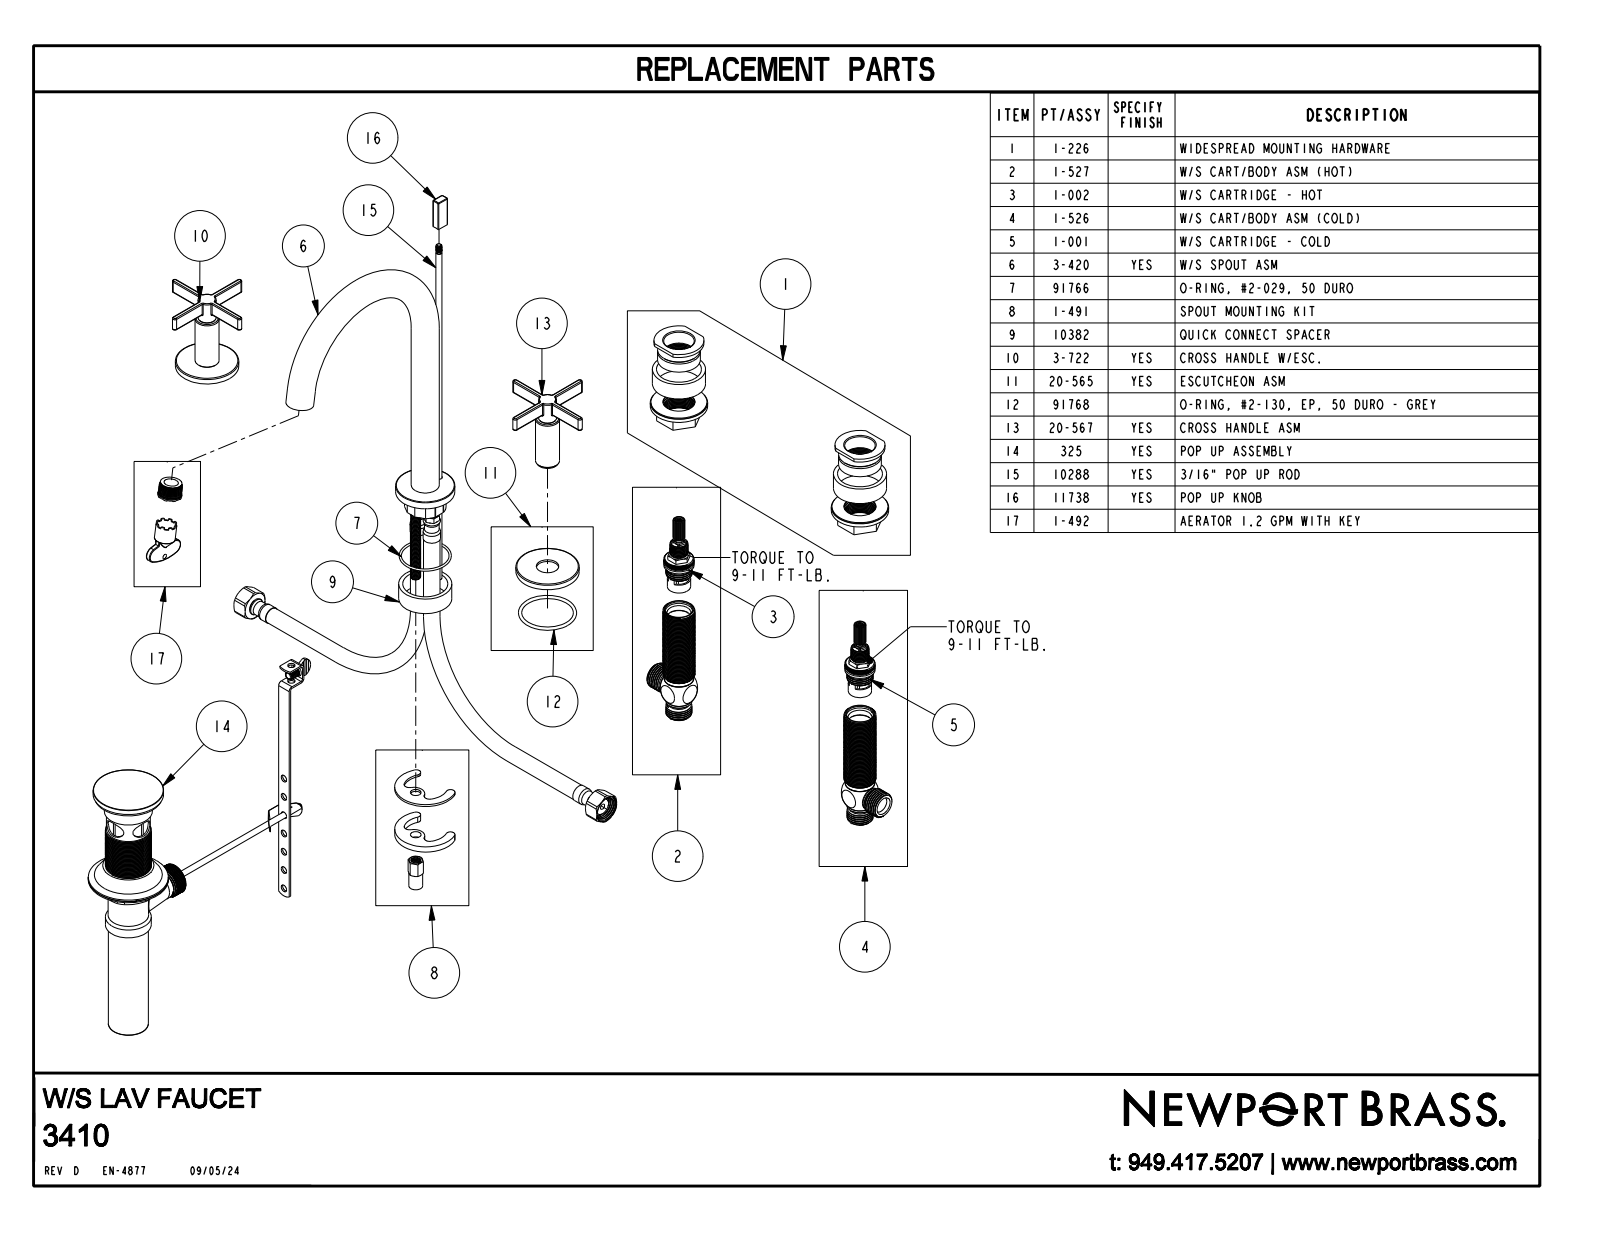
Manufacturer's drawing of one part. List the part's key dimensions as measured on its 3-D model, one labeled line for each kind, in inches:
Part name (STEP PRODUCT): 3410
STEP written by: CREO PARAMETRIC BY PTC INC, 2019352 (CONFIG_CONTROL_DESIGN)
Units: inches
Bodies: 4 solids, 220 faces (44 planar, 92 cylindrical, 84 other)
Overall size (bounding box): 11 × 9.444 × 7.476
Volume: 13.25 in³ · Surface area: 85.76 in²
Round holes (diameter × count): ⌀0.73 ×1
Round bosses / shafts (diameter × count): ⌀1.98 ×2, ⌀0.875 ×2, ⌀0.75 ×2, ⌀0.73 ×2, ⌀0.563 ×2, ⌀0.51 ×2, ⌀1.85 ×1
Partial cylindrical surfaces — rounded edges, fillets, slot ends (radius × count): R0.03 ×28, R0.075 ×8, R0.02 ×6, R0.47 ×1, R0.876 ×1
Main face-to-face distances: 0.2, 0.25, 0.05, 0.15, 0.15, 8, 2.551, 2.351, 2.301, 8.15
